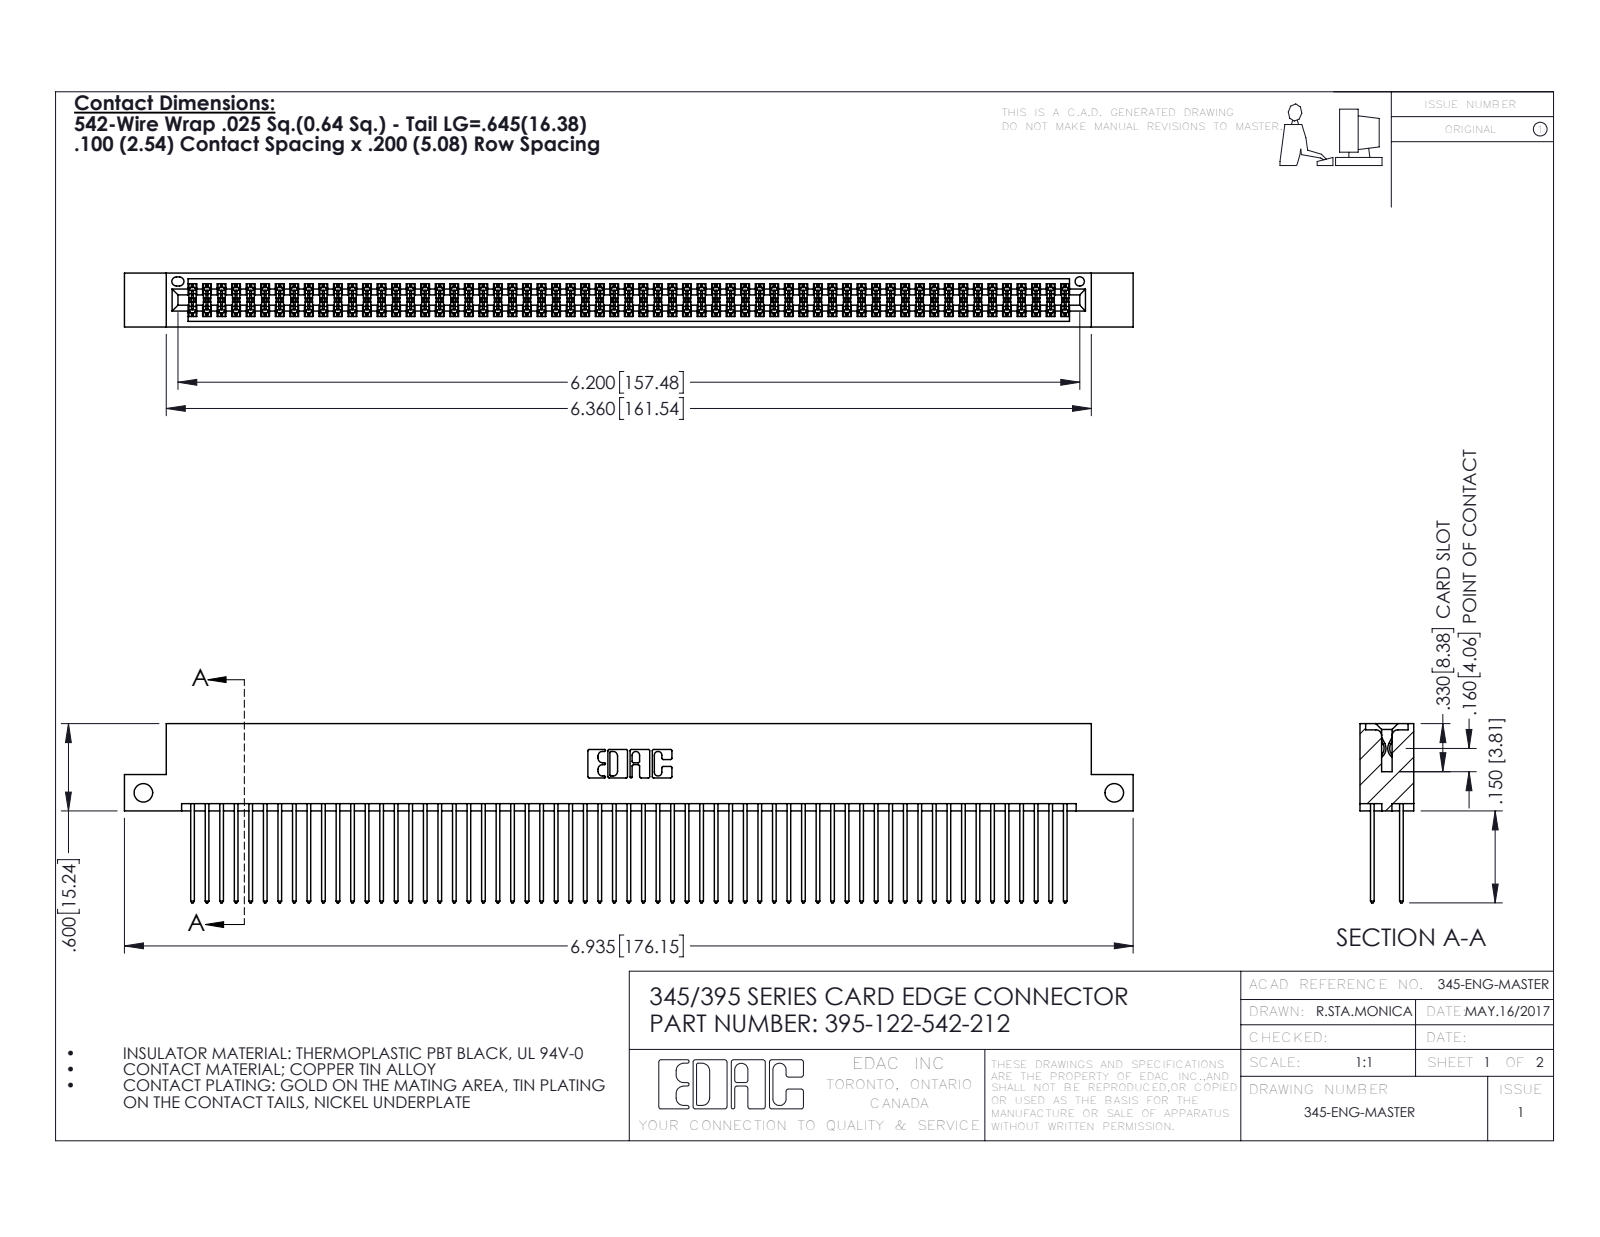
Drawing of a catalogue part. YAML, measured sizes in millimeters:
part_name: "345-292-001_345-293-142; 395-122-542-212; 345 Part_Flush Mounting Lugs - Side Mount"
step_written_by: "SolidWorks 2016 (CONFIG_CONTROL_DESIGN)"
units: millimeters
bodies: {solids: 123, faces: 6226, planar: 4106, cylindrical: 2120, other: 0}
overall_size: [176.1, 31.3, 9.4]
volume: 17760
surface_area: 29150
round_holes:
  - {diameter: 3.3, count: 2}
  - {diameter: 1.6, count: 1}
partial_cylinders:
  - {radius: 0.2, count: 183}
  - {radius: 0.3, count: 122}
  - {radius: 0.3, count: 22}
  - {radius: 0.2, count: 6}
  - {radius: 0.8, count: 6}
  - {radius: 0.7, count: 3}
  - {radius: 0.4, count: 2}
  - {radius: 0.5, count: 2}
face_to_face_distances: [7.6, 1.8, 5.1, 2.5, 6.9, 0.6, 5.7, 9.4, 4.4, 3.8]
hole_center_spacings: [169.5]
